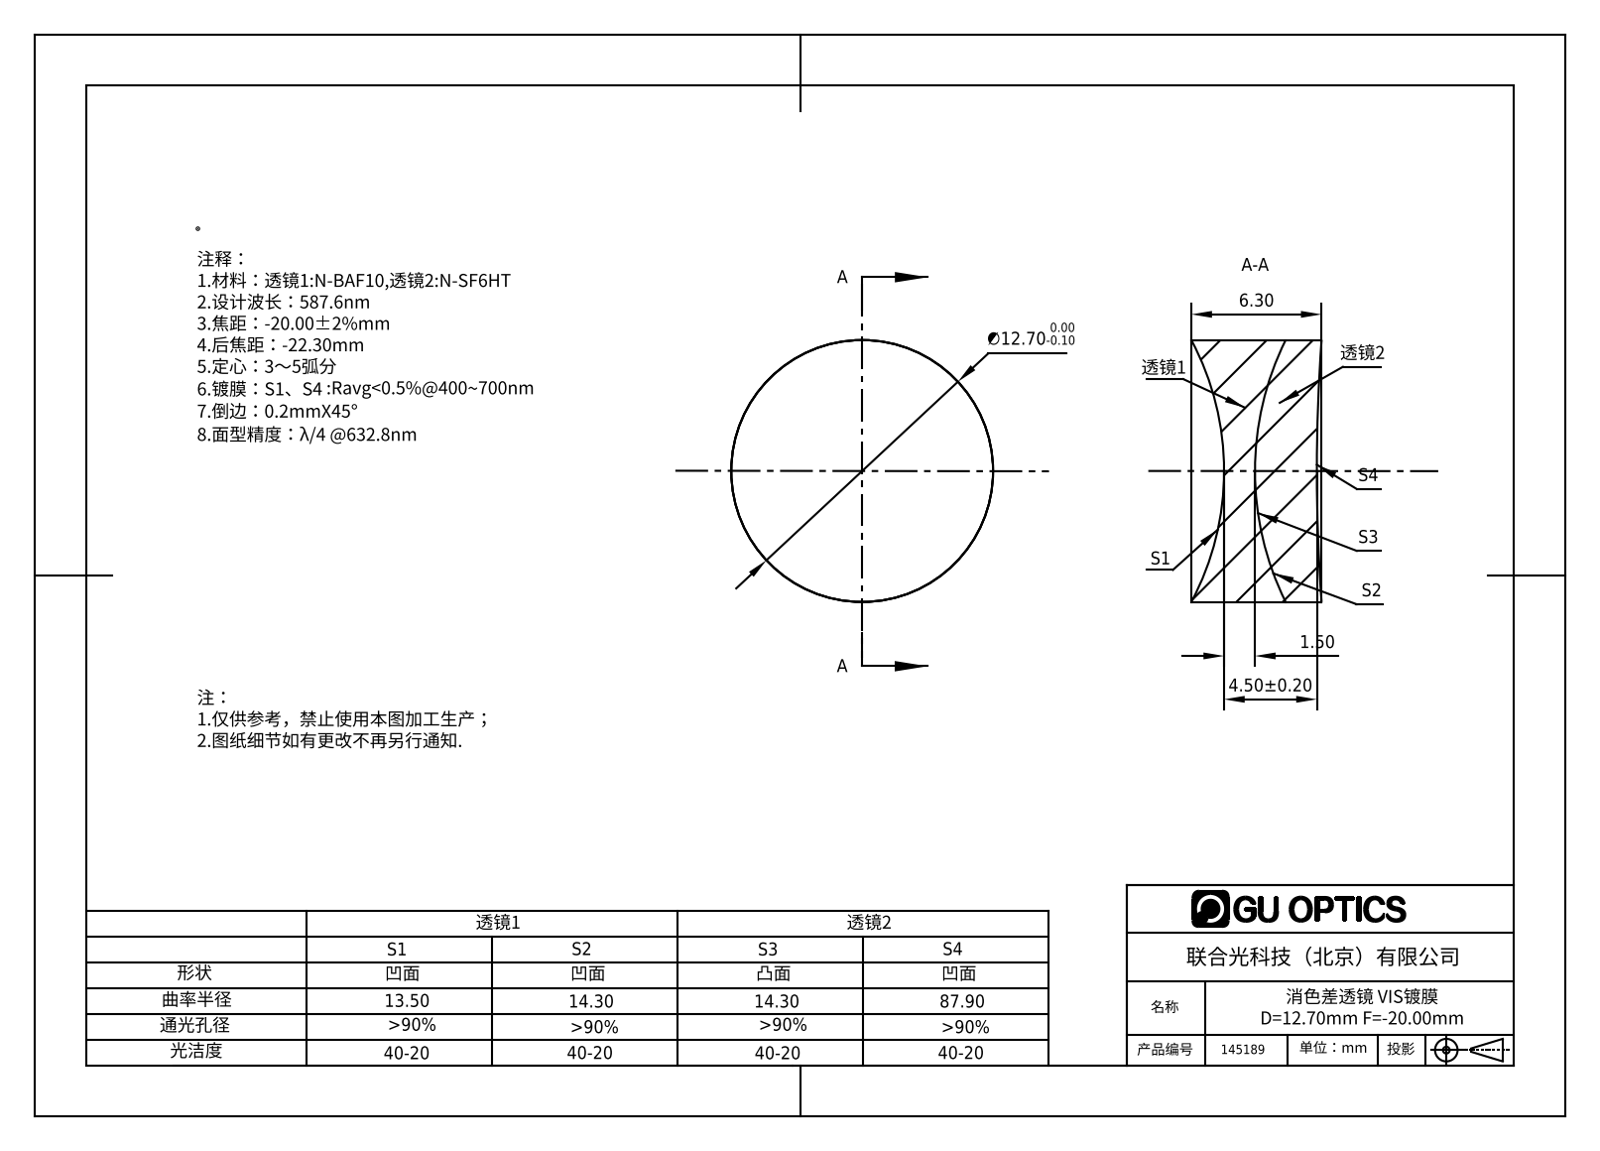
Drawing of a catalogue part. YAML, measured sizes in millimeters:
part_name: "145189"
step_written_by: "SolidWorks 2016 (AUTOMOTIVE_DESIGN)"
units: millimeters
bodies: {solids: 2, faces: 12, planar: 0, cylindrical: 4, other: 8}
overall_size: [12.7, 12.7, 6.32]
volume: 683
surface_area: 781
round_bosses_or_shafts:
  - {diameter: 12.7, count: 1}
